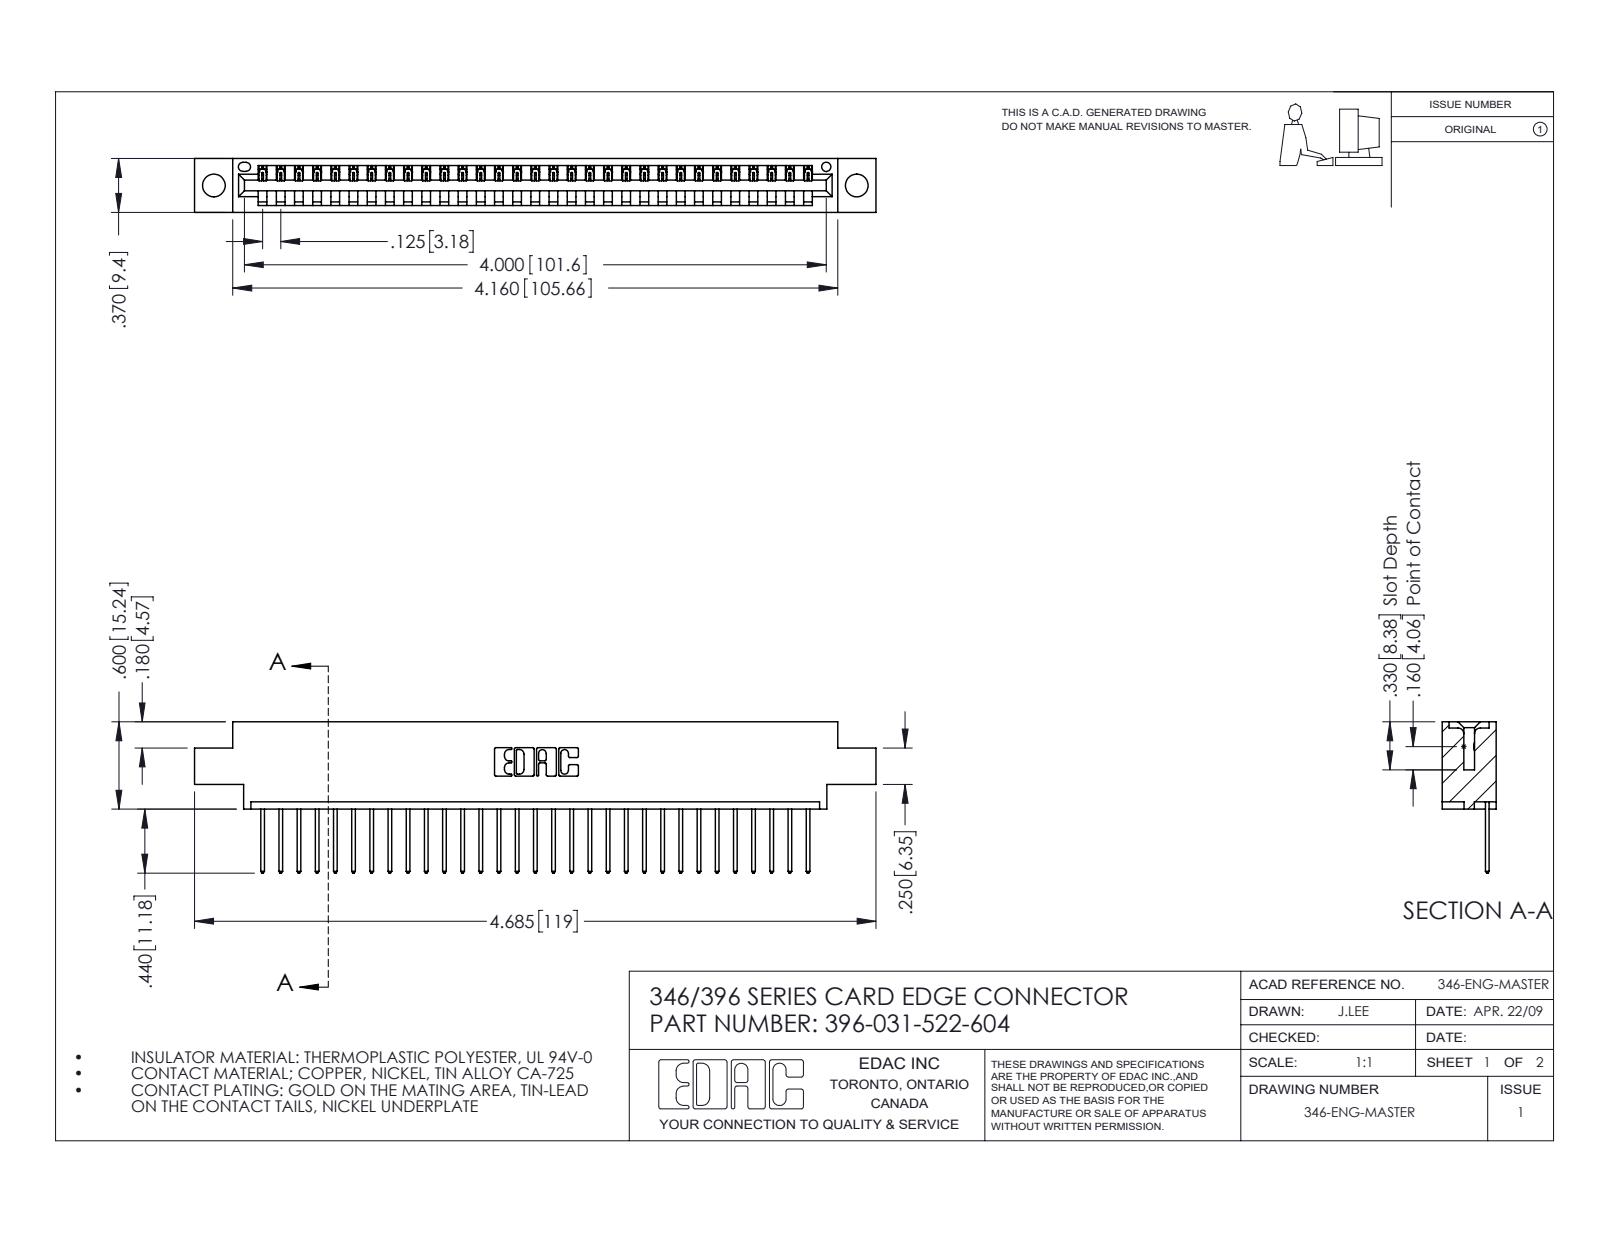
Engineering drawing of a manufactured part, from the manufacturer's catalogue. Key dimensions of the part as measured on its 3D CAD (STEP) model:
Part name (STEP PRODUCT): 346 Part_0.170 Offset - 0.156 Dia-TH; 396-031-522-604; 345-292-001_345-293-122
STEP written by: SolidWorks 2016 (CONFIG_CONTROL_DESIGN)
Units: inches
Bodies: 32 solids, 1924 faces (1320 planar, 604 cylindrical, 0 other)
Overall size (bounding box): 4.685 × 1.04 × 0.37
Volume: 0.676 in³ · Surface area: 21.4 in²
Round holes (diameter × count): ⌀0.156 ×2, ⌀0.064 ×1
Partial cylindrical surfaces — rounded edges, fillets, slot ends (radius × count): R0.006 ×62, R0.01 ×62, R0.01 ×22, R0.007 ×6, R0.031 ×6, R0.026 ×3, R0.031 ×2, R0.04 ×2
Main face-to-face distances: 0.048, 0.322, 0.37, 0.25, 0.072, 0.298, 0.025, 0.148, 0.222, 0.1
Hole centre spacings: 0.246, 4.212, 4.42
